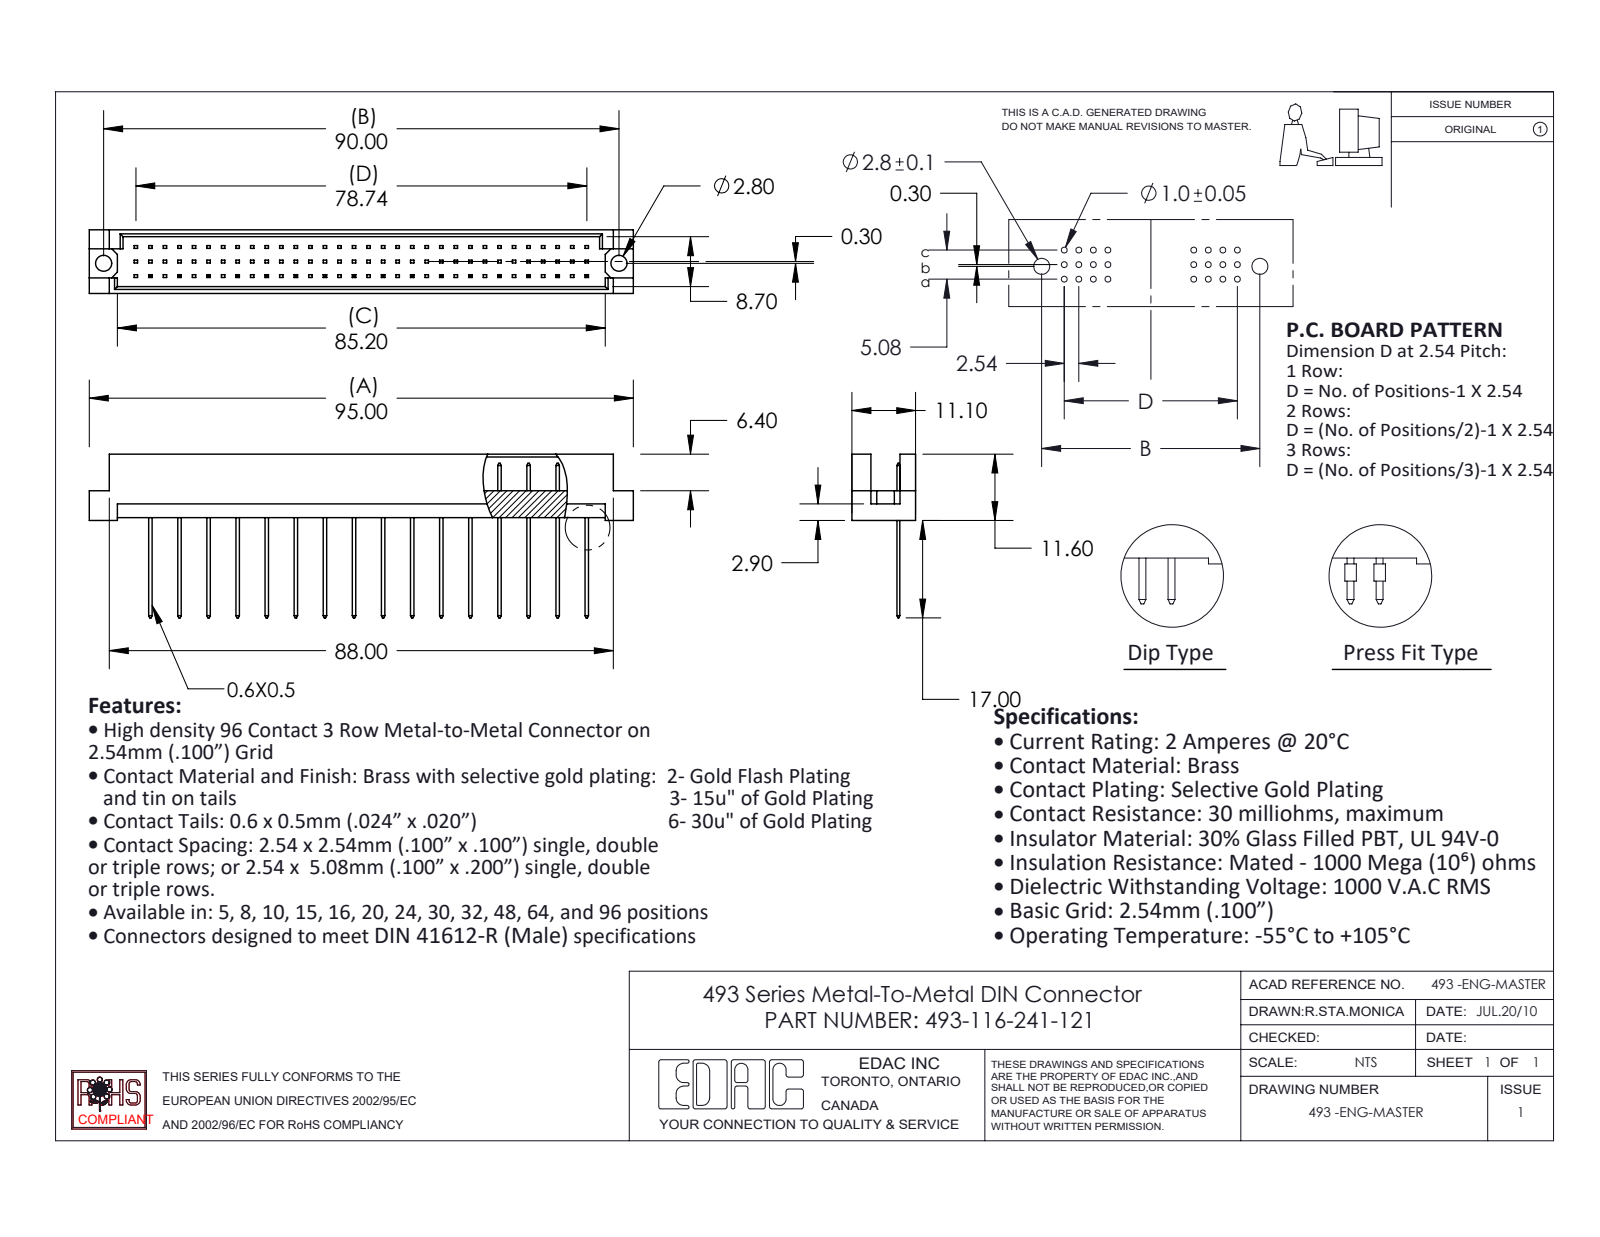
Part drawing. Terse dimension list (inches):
name: 493-116-241-622; 493-290_41; 493 Part_96
written by: SolidWorks 2020 (CONFIG_CONTROL_DESIGN)
unit: in
bodies: 17 solids, 660 faces (656 planar, 4 cylindrical, 0 other)
size: 3.74 × 1.126 × 0.437
volume: 0.353 in³; area: 11.5 in²
holes: 2× ⌀0.11
face distances: 0.047, 0.39, 0.437, 0.343, 0.185, 0.02, 0.2, 0.128, 0.309, 0.081
hole spacings: 3.543
